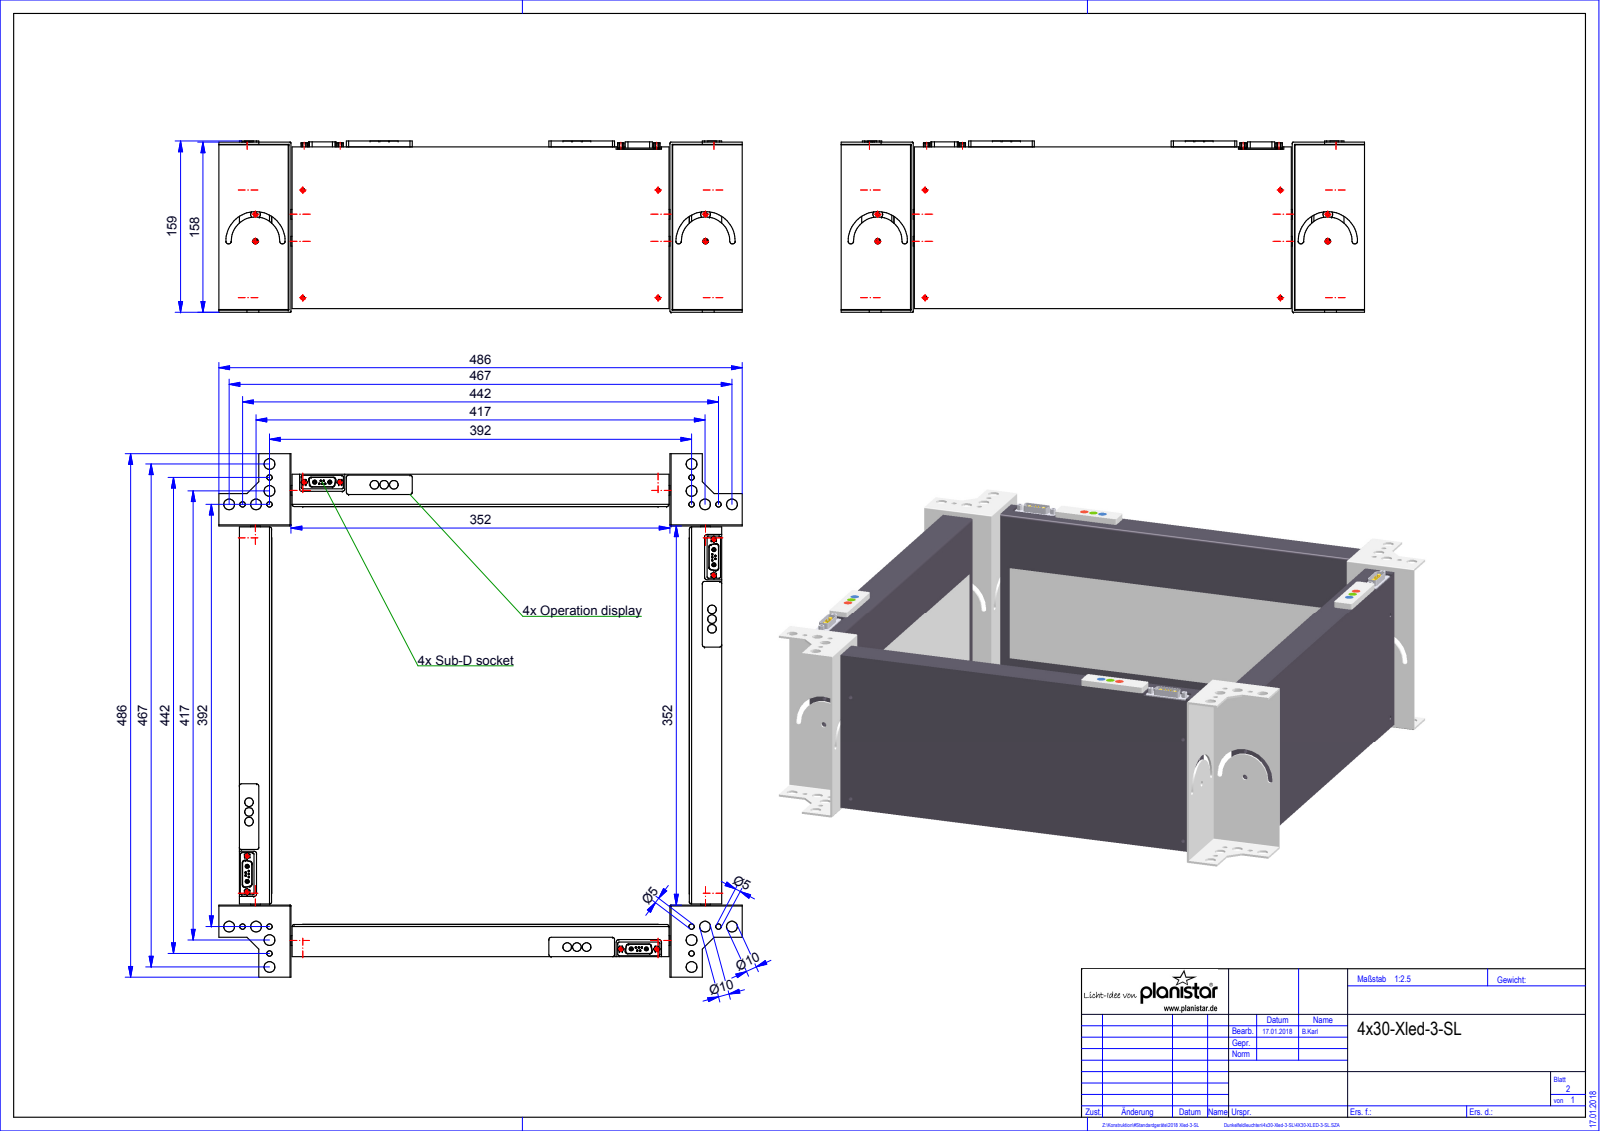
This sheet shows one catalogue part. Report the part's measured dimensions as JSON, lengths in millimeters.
{"part_name": "Root; Baugruppe_Xled-2-VD; QUADER_0; Baugruppe_Baugruppe (+6 more)", "step_written_by": "HiCAD 2015 2002.1 Build 408 (AUTOMOTIVE_DESIGN)", "units": "millimeters", "bodies": {"solids": 52, "faces": 892, "planar": 400, "cylindrical": 408, "other": 84}, "overall_size": [486, 486, 159.05], "volume_mm3": 6526000, "surface_area_mm2": 774895, "round_holes": [[3.3, 16], [4, 16], [5, 16], [10, 16], [2.5, 8], [3, 8]], "round_bosses_or_shafts": [[1, 20], [8, 12], [9, 8], [3.6, 8]], "partial_cylinders_radius": [[0.2, 48], [2, 32], [2.5, 32], [1.5, 16], [2.1, 16], [0.5, 12], [1, 12], [22.5, 4]], "face_to_face_distances": [30.1, 417.9, 448, 2, 418, 30, 387.9, 18, 400, 48], "hole_center_spacings": [12.5, 25, 392.2, 392, 392.8, 429.5, 581.49, 442]}
